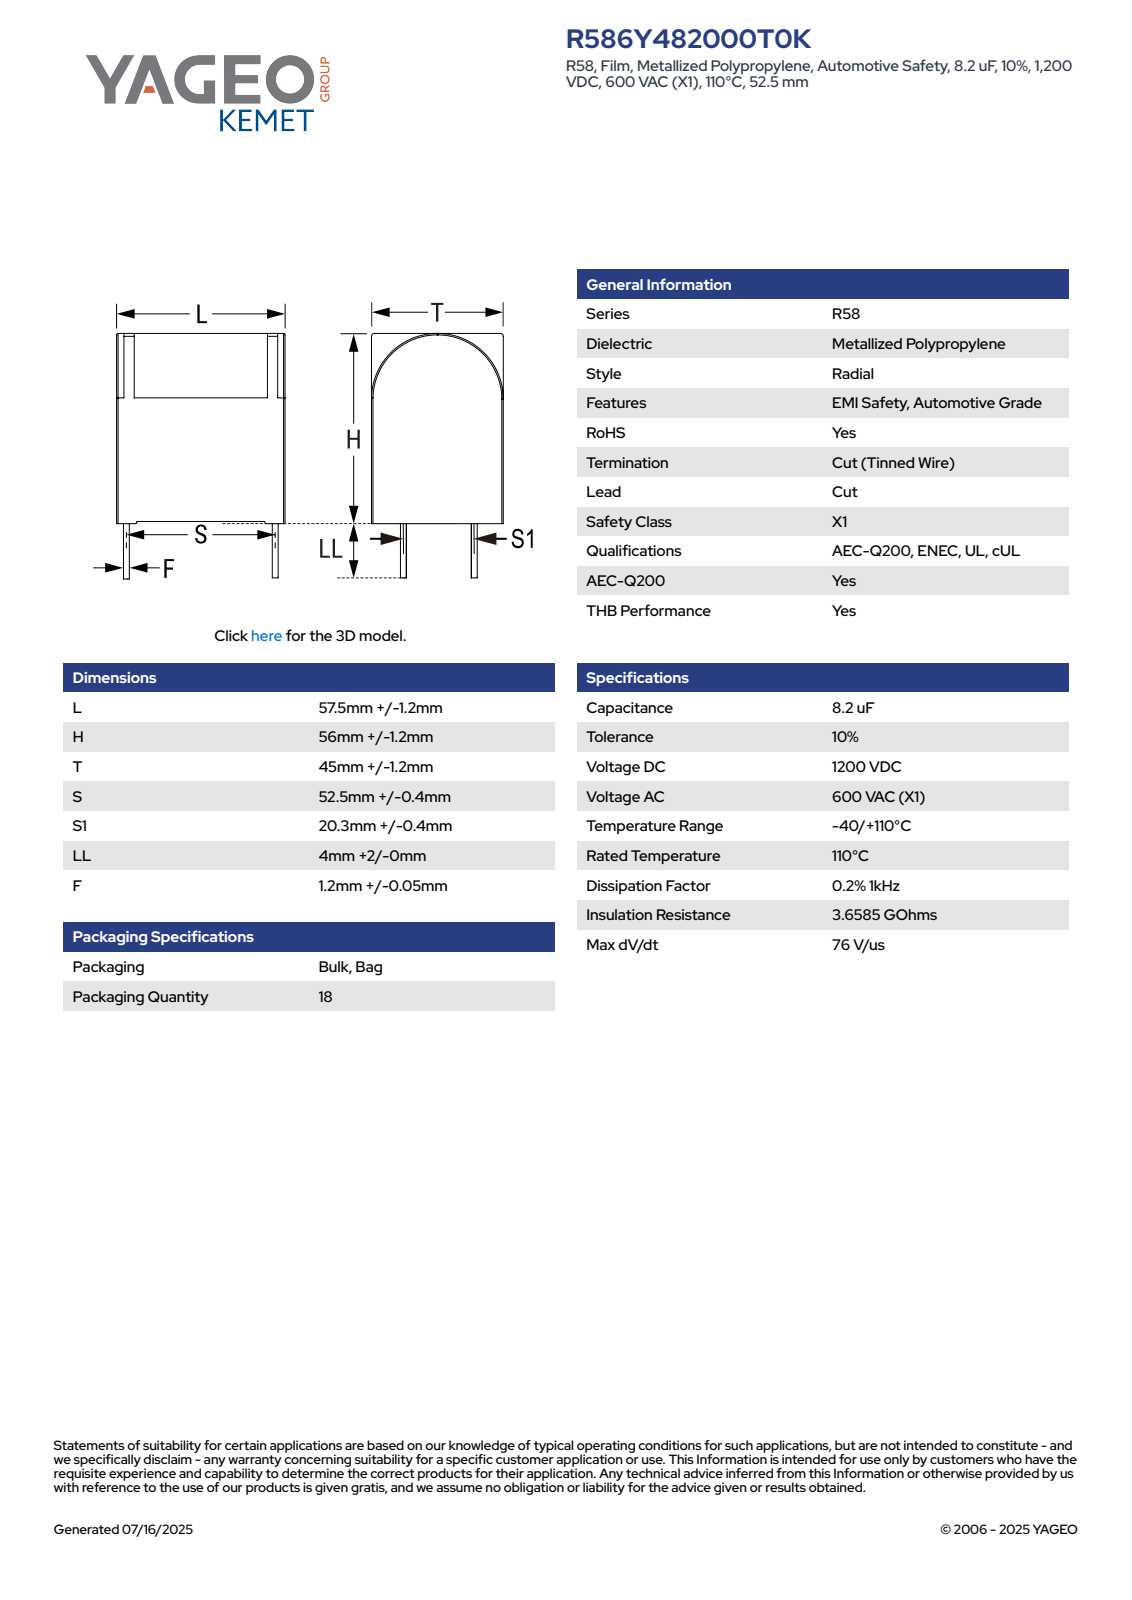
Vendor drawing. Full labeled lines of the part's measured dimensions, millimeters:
Part name (STEP PRODUCT): CFP_RB4A_57.5X56X45_L58.7H57.2T46.2S52.5S120.3LL6F1.25
STEP written by: SolidWorks 2021 (AUTOMOTIVE_DESIGN)
Units: millimetres
Bodies: 4 solids, 103 faces (92 planar, 11 cylindrical, 0 other)
Overall size (bounding box): 63.2 × 58.7 × 46.2
Volume: 141 289 mm³ · Surface area: 17 394 mm²
Round bosses / shafts (diameter × count): ⌀1.25 ×4
Partial cylindrical surfaces — rounded edges, fillets, slot ends (radius × count): R23.1 ×1
Main face-to-face distances: 58.7, 46.2, 55.52, 3.5, 55.2, 11.35, 47.35, 7.85, 43.85, 1.68
